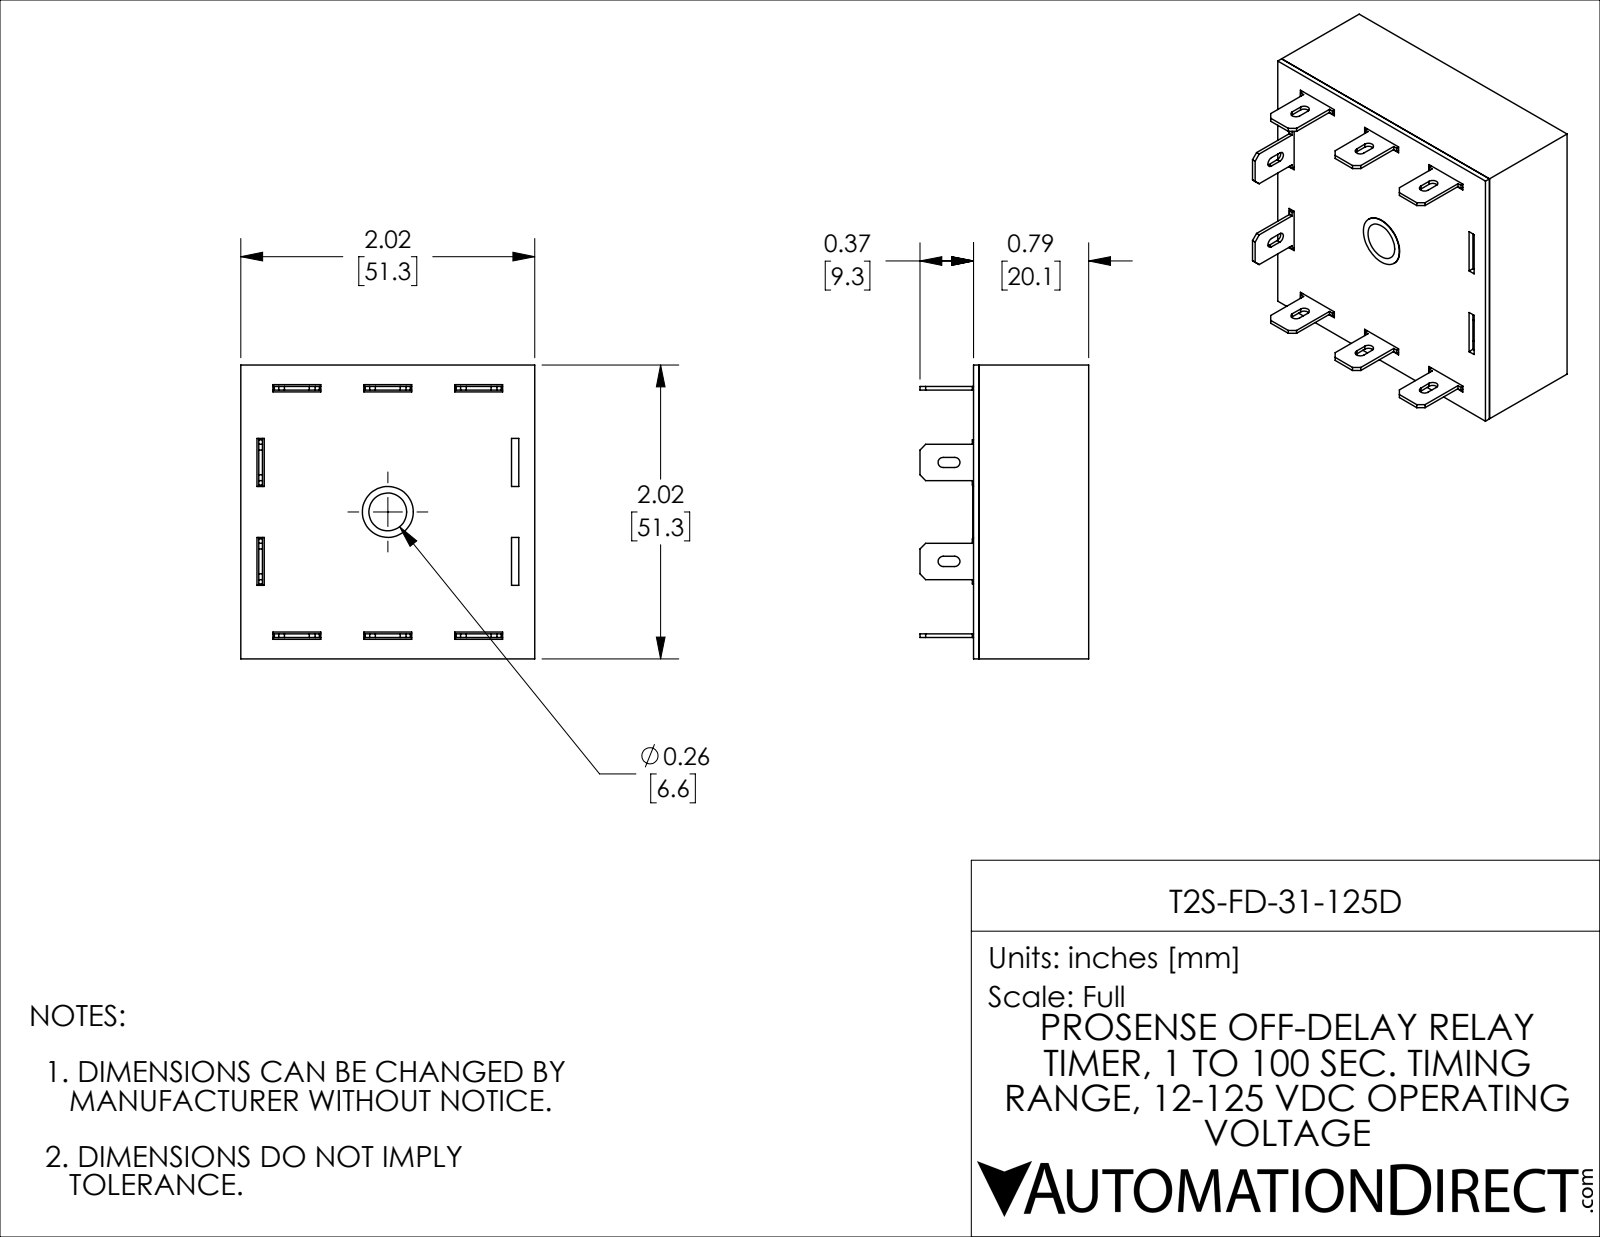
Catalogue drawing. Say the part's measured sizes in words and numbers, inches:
The part is named "T2S-FD-31-125D". Its 3-D file was written by "SolidWorks 2021 (CONFIG_CONTROL_DESIGN)". It is 10 solids with 256 faces: 234 planar, 20 cylindrical and 2 other. Overall it measures 2.02 by 2.02 by 1.16 inches. Its volume is 0.674 cubic inches and its surface area 35.37 square inches. Round holes: 1 of diameter 0.35. Partial cylindrical surfaces (rounded edges, fillets, slot ends): 10 of radius 0.035. The main face-to-face distances are 0.045, 1.975, 0.754, 0.792, 0.038, 0.709, 0.747, 2.02, 1.93, 0.147.
